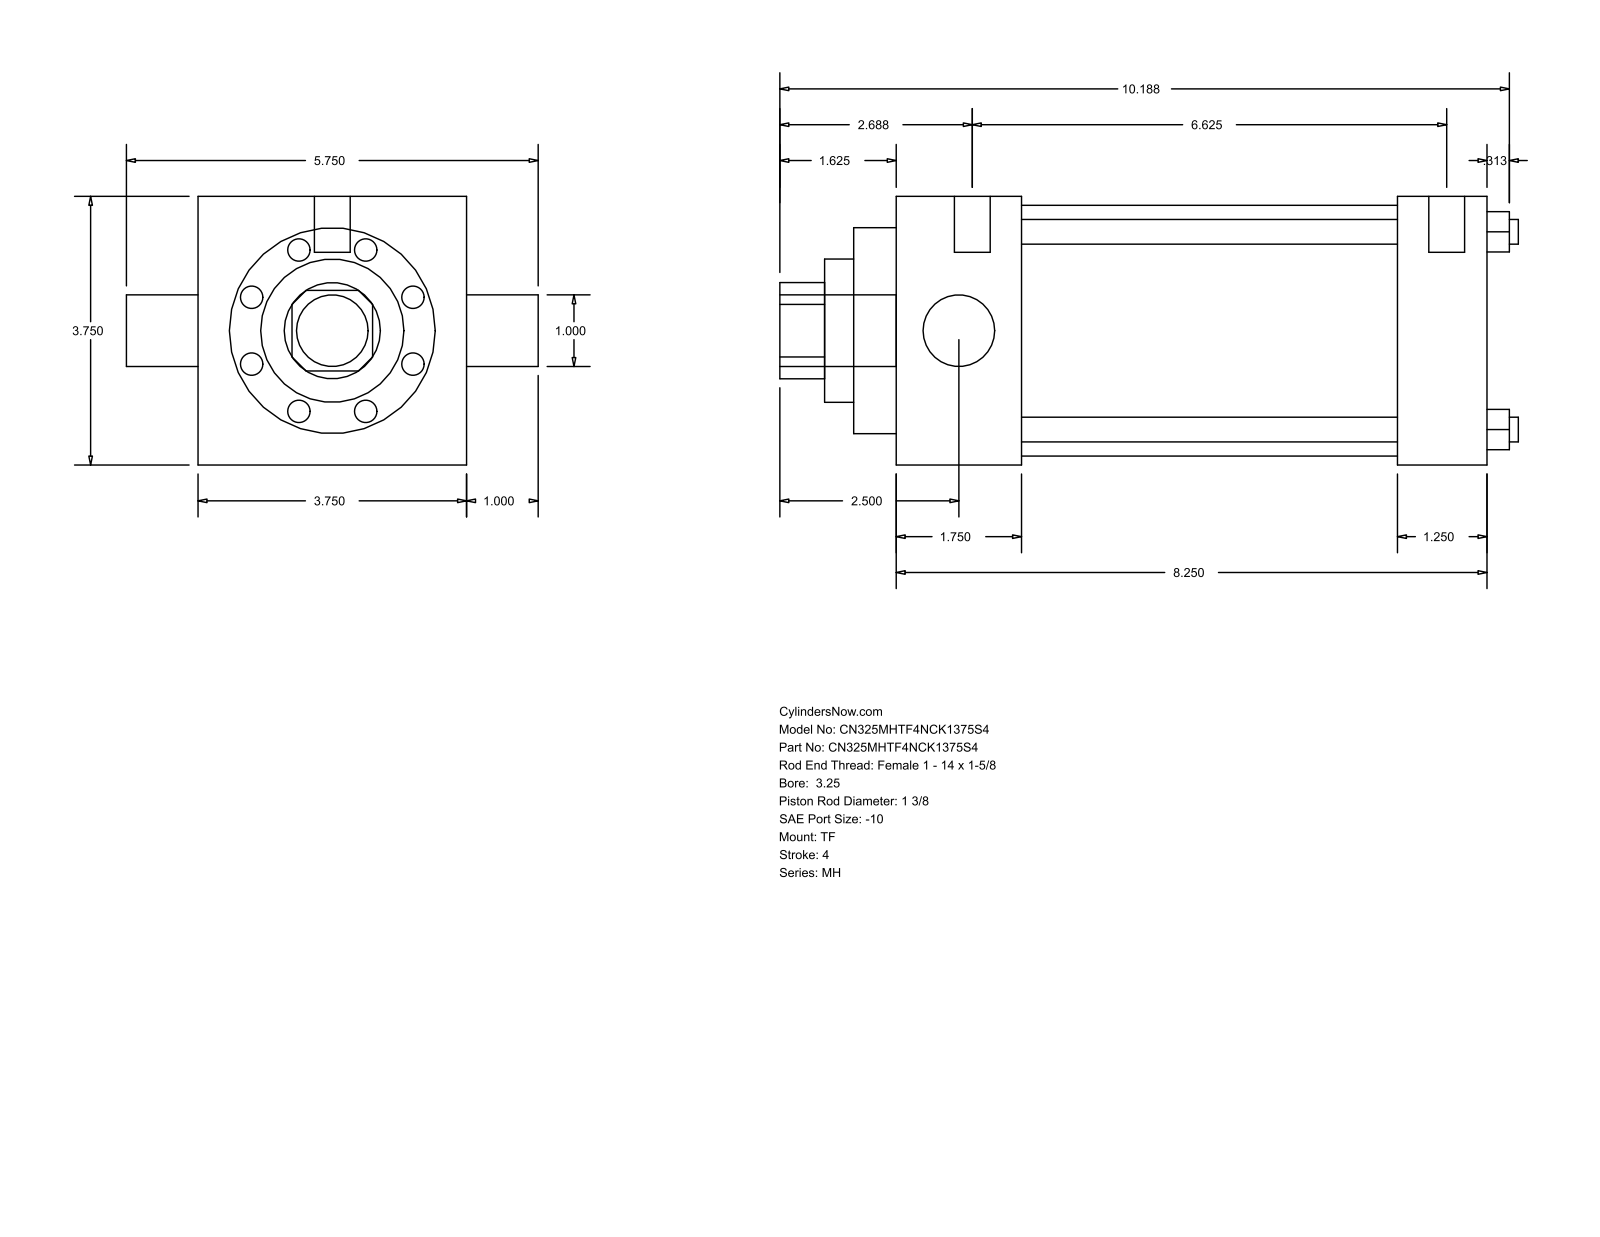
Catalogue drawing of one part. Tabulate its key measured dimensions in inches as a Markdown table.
| quantity | value |
| --- | --- |
| part name | MH_TF__0325_1.375 |
| STEP written by | GSSL Pune (CONFIG_CONTROL_DESIGN) |
| units | inches |
| bodies | 0 solids, 86 faces (61 planar, 25 cylindrical, 0 other) |
| overall size | 10.313 × 5.75 × 3.75 |
| round holes (diameter × count) | 0.345 × 4, 1 × 1, 1.375 × 1, 2 × 1, 2.875 × 1, 3.5 × 1 |
| round bosses / shafts (diameter × count) | 0.219 × 3, 0.5 × 2, 1 × 1 |
| partial cylindrical surfaces (radius × count) | 0.672 × 1 |
| main face-to-face distances | 3.75, 8.25, 1.75, 7, 5.25, 6.5, 1.25, 0.594, 2.344, 7.594 |
| hole center spacings | 1.952, 2.76, 3.903 |
